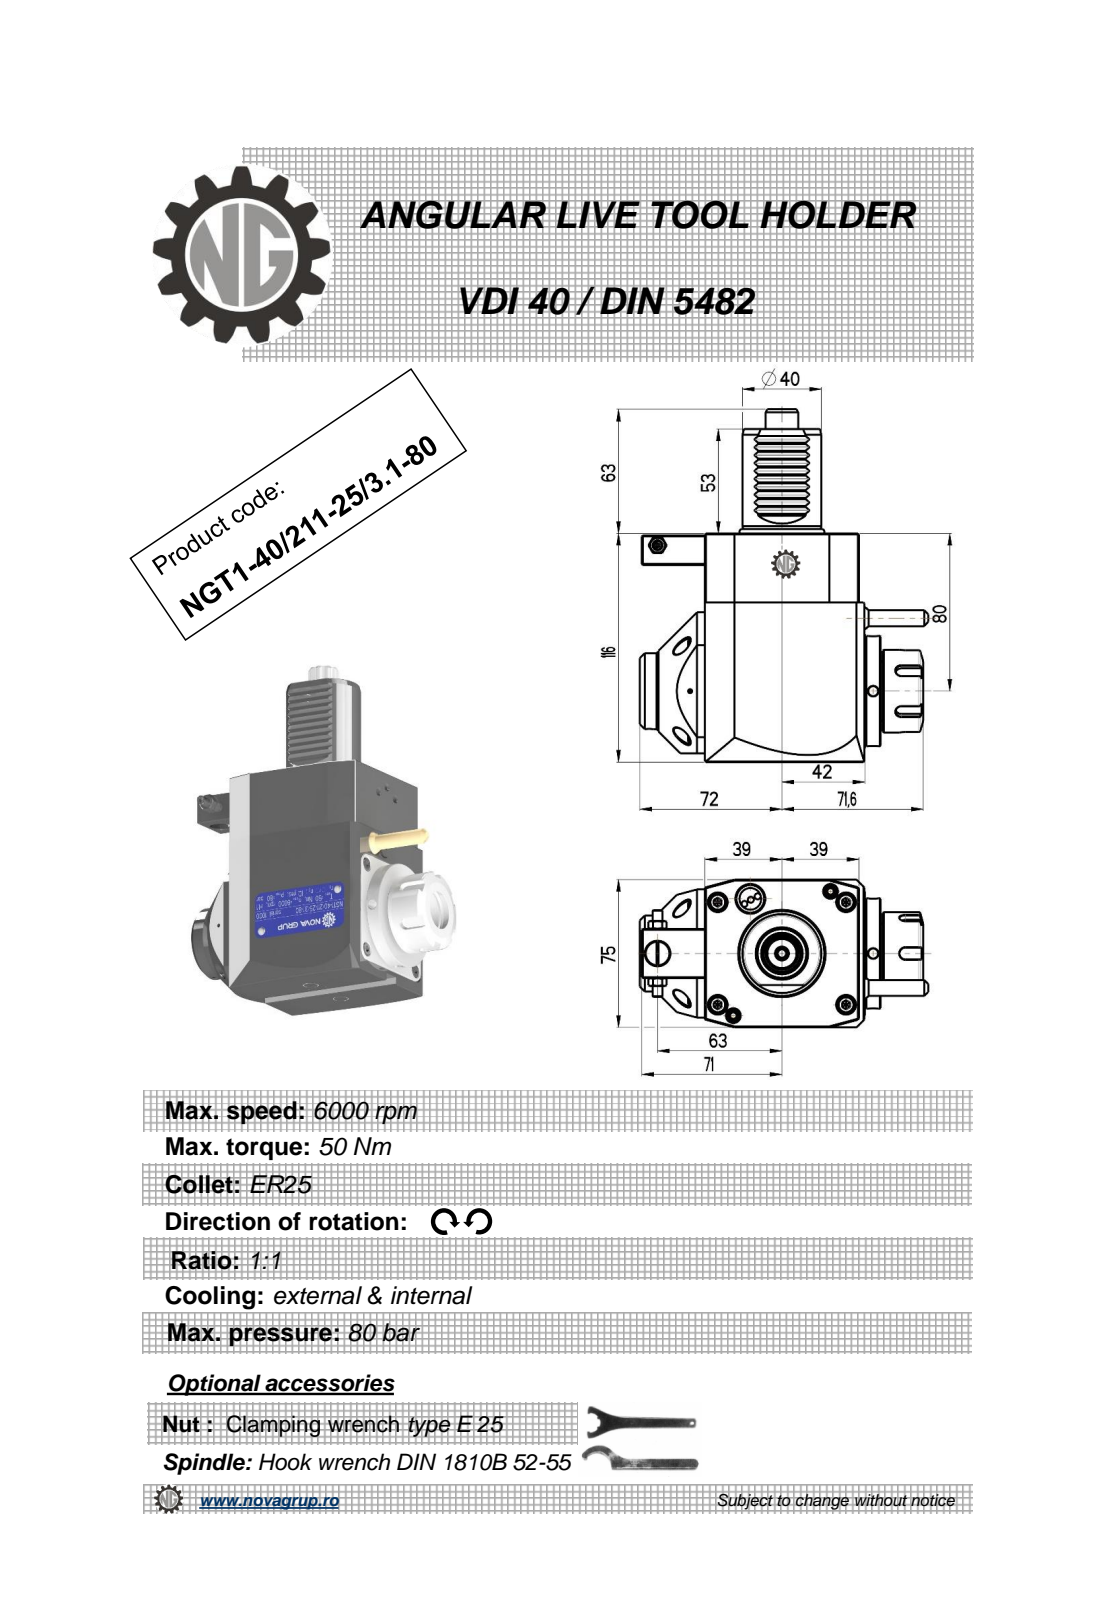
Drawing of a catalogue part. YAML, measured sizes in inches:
part_name: "NGT1_40_211_25_3_1_80"
step_written_by: "PRO/ENGINEER BY PARAMETRIC TECHNOLOGY CORPORATION, 2010280 (CONFIG_CONTROL_DESIGN)"
units: inches
bodies: {solids: 1, faces: 473, planar: 183, cylindrical: 124, other: 166}
overall_size: [7.047, 5.754, 2.953]
volume: 53.97
surface_area: 110.5
round_holes:
  - {diameter: 0.197, count: 3}
  - {diameter: 0.165, count: 2}
  - {diameter: 0.118, count: 1}
  - {diameter: 0.209, count: 1}
  - {diameter: 0.374, count: 1}
  - {diameter: 0.472, count: 1}
  - {diameter: 0.799, count: 1}
round_bosses_or_shafts:
  - {diameter: 2.205, count: 1}
  - {diameter: 1.693, count: 1}
  - {diameter: 1.654, count: 1}
  - {diameter: 1.575, count: 1}
  - {diameter: 1.516, count: 1}
  - {diameter: 1.299, count: 1}
  - {diameter: 0.441, count: 1}
  - {diameter: 0.353, count: 1}
partial_cylinders:
  - {radius: 0.119, count: 18}
  - {radius: 0.01, count: 12}
  - {radius: 0.012, count: 10}
  - {radius: 0.009, count: 6}
  - {radius: 0.118, count: 5}
  - {radius: 0.02, count: 1}
  - {radius: 0.266, count: 1}
  - {radius: 0.325, count: 1}
face_to_face_distances: [2.953, 4.567, 3.189, 3.071, 0.118, 0.433, 0.315, 4.37, 3.181, 0.11]
hole_center_spacings: [1.558, 1.611, 1.821, 2.48, 2.854, 4.301, 5.195]
